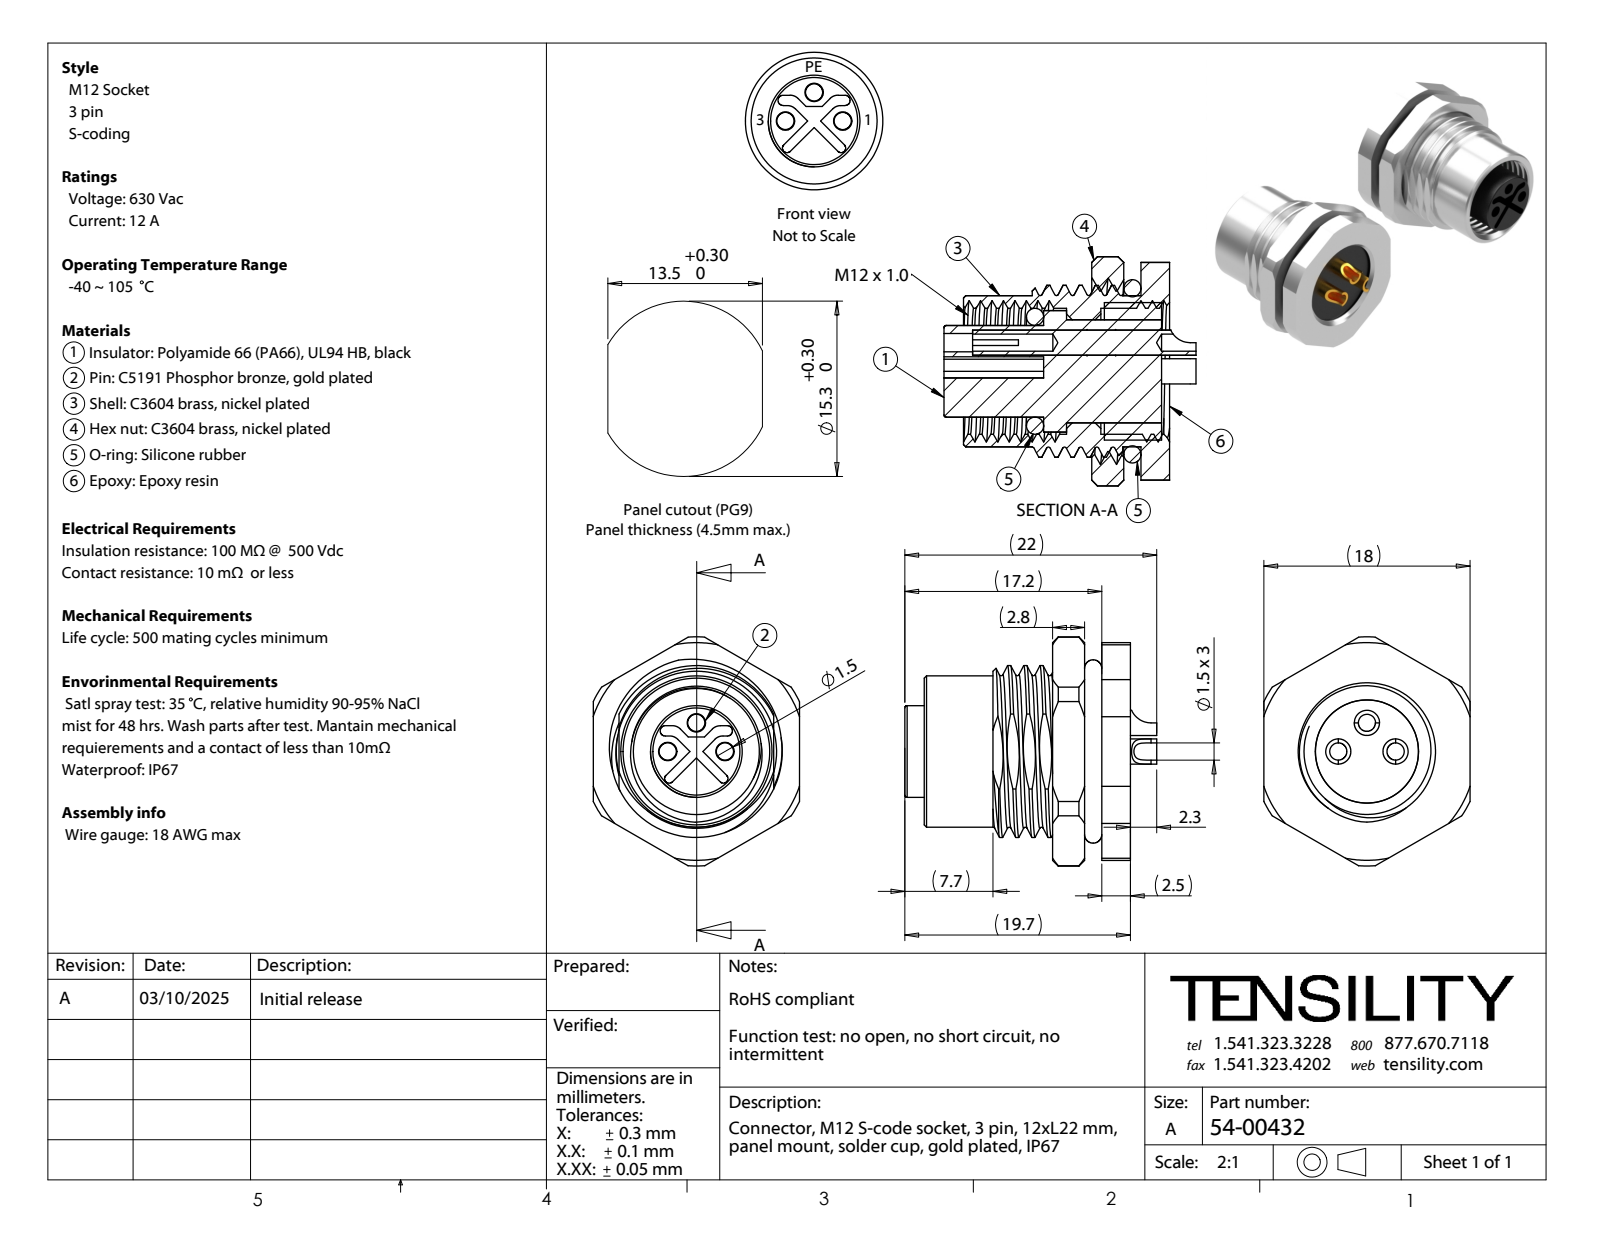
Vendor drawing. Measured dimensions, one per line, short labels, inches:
name: 54-00432-05; 54-00432-01; 54-00432-02; 54-00432-03 (+3 more)
written by: SolidWorks 2021 (CONFIG_CONTROL_DESIGN)
unit: in
bodies: 9 solids, 299 faces (98 planar, 122 cylindrical, 79 other)
size: 0.866 × 0.787 × 0.709
volume: 0.174 in³; area: 8.655 in²
holes: 3× ⌀0.059, 3× ⌀0.063, 1× ⌀0.354, 1× ⌀0.433, 1× ⌀0.551
bosses: 3× ⌀0.087, 1× ⌀0.52, 1× ⌀0.472, 1× ⌀0.417, 1× ⌀0.315
rounds: 4× R0.039, 3× R0.073, 2× R0.016, 2× R0.018, 1× R0.295, 1× R0.374, 1× R0.394
face distances: 0.098, 0.709, 0.13, 0.197, 0.028, 0.071, 0.031, 0.157, 0.169, 0.059
hole spacings: 0.098, 0.139, 0.197
